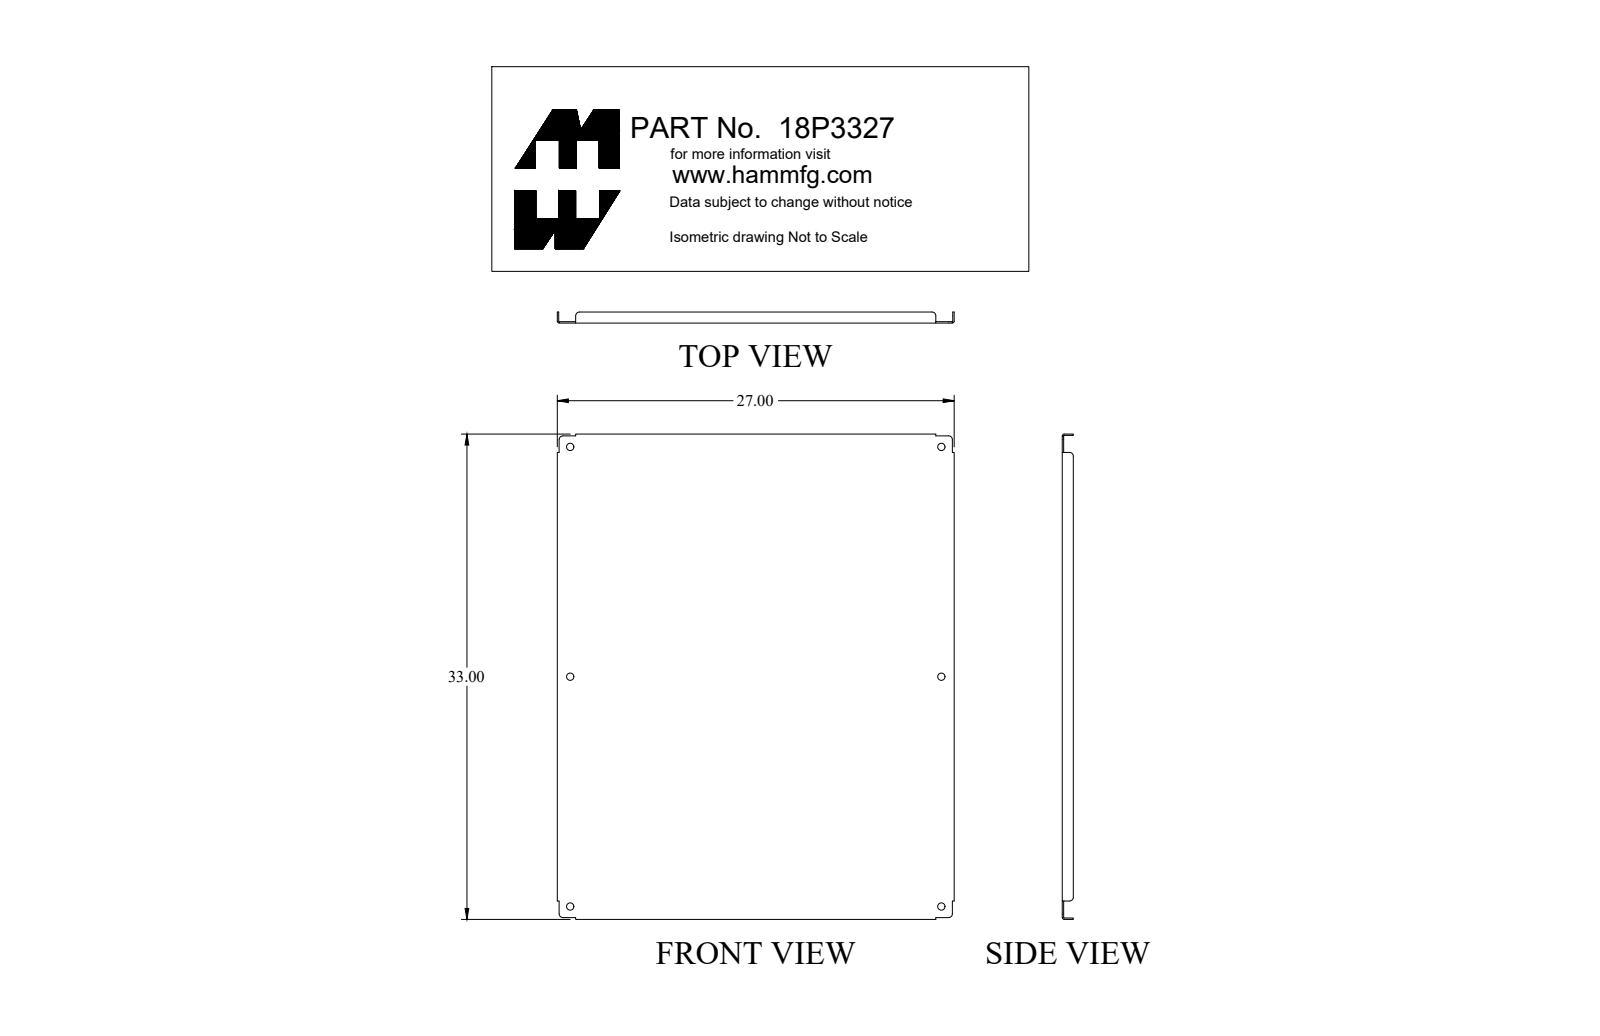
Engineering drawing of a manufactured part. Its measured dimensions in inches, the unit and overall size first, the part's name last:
Units: inches
Overall size (bounding box): 33 × 27 × 0.75
Round holes (diameter × count): ⌀0.5 ×6
Partial cylindrical surfaces — rounded edges, fillets, slot ends (radius × count): R0.25 ×8, R0.03 ×4, R0.125 ×4
Main face-to-face distances: 0.095, 26.905, 32.905, 26.81, 27, 33, 32.81, 0.75, 0.655, 0.125
Hole centre spacings: 15.625, 29.694, 25.25, 31.25, 40.177
Volume: 90.9 in³ · Surface area: 1 926 in²
Bodies: 1 solid, 62 faces (30 planar, 32 cylindrical, 0 other)
Part name (STEP PRODUCT): 18P3327_Default
STEP written by: SolidWorks 2018 (CONFIG_CONTROL_DESIGN)
